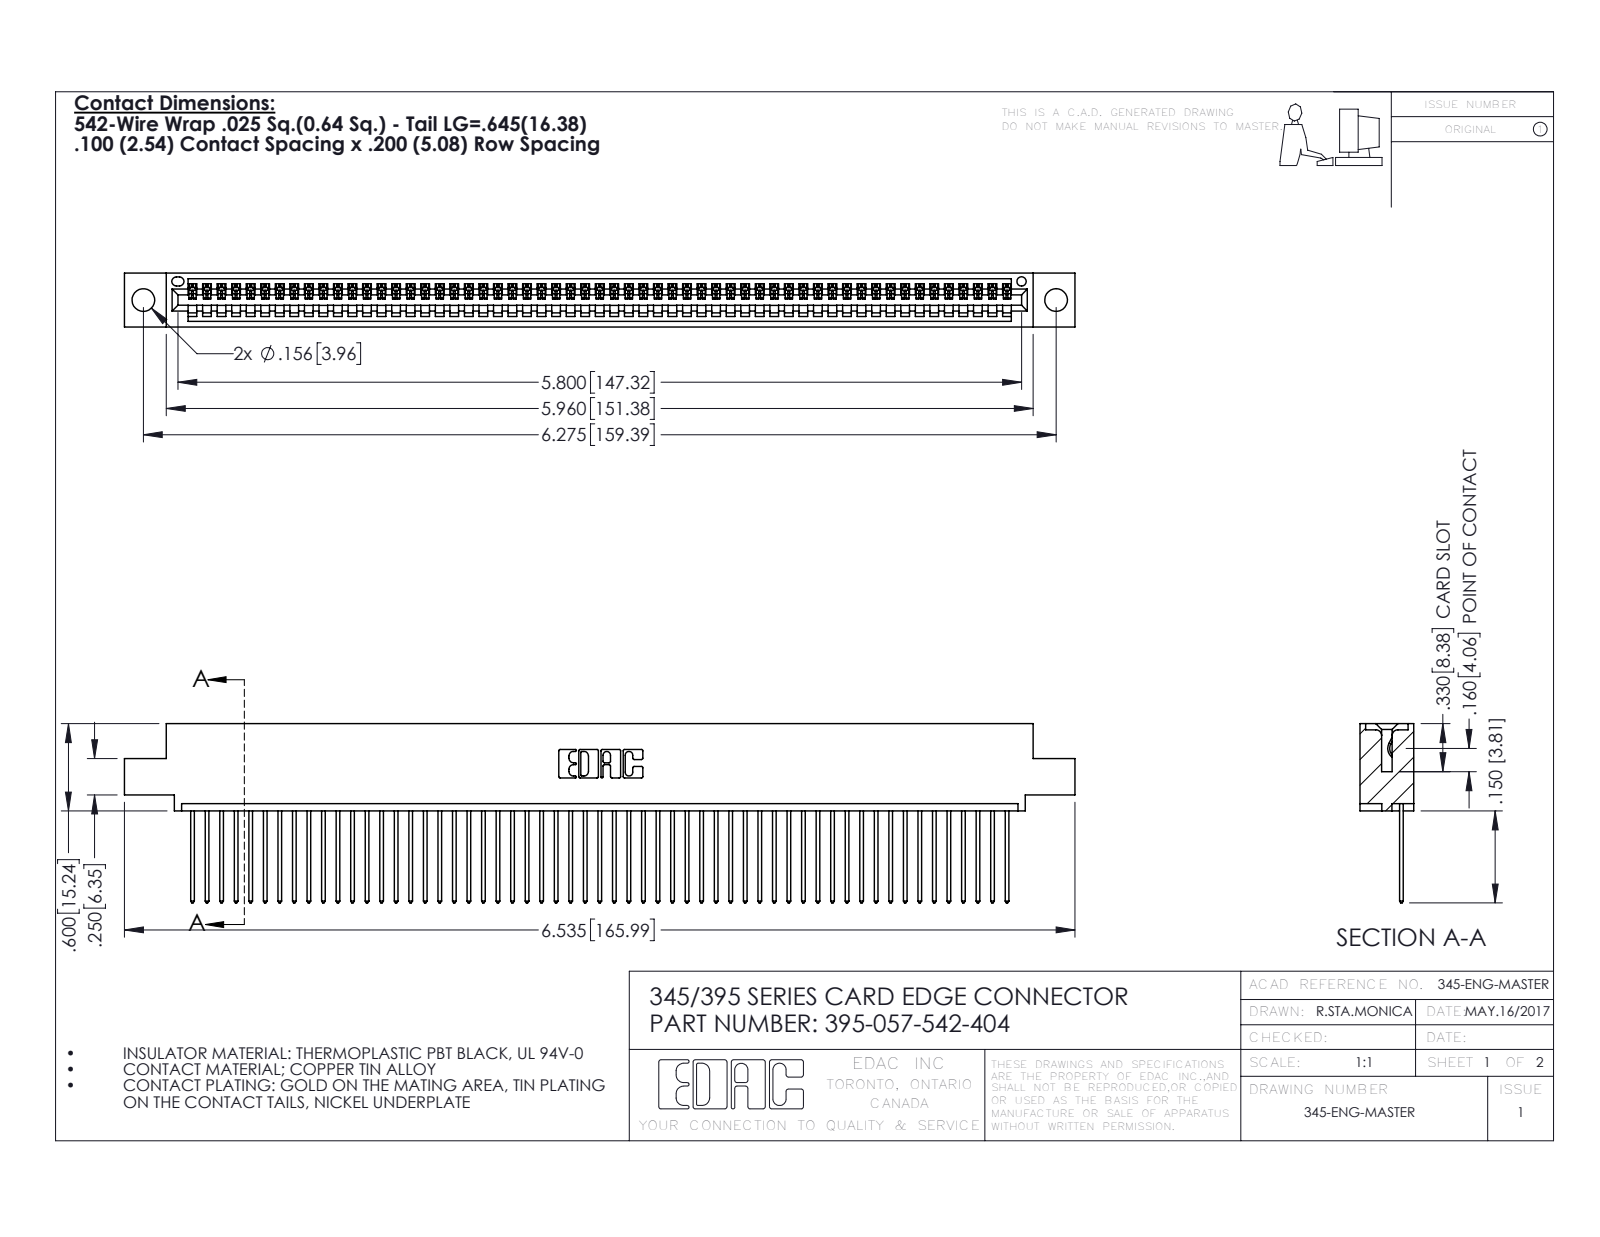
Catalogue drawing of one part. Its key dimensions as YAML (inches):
part_name: "395-057-542-404; 345-292-001_345-293-142; 345 Part_0.110 Offset - 0.156 Dia-TH"
step_written_by: "SolidWorks 2016 (CONFIG_CONTROL_DESIGN)"
units: inches
bodies: {solids: 58, faces: 3436, planar: 2364, cylindrical: 1072, other: 0}
overall_size: [6.535, 1.232, 0.37]
volume: 0.967
surface_area: 34.05
round_holes:
  - {diameter: 0.156, count: 2}
  - {diameter: 0.064, count: 1}
partial_cylinders:
  - {radius: 0.006, count: 114}
  - {radius: 0.01, count: 114}
  - {radius: 0.01, count: 22}
  - {radius: 0.007, count: 6}
  - {radius: 0.031, count: 6}
  - {radius: 0.026, count: 3}
  - {radius: 0.031, count: 2}
  - {radius: 0.04, count: 2}
face_to_face_distances: [0.072, 0.298, 0.098, 0.272, 0.025, 0.37, 0.2, 0.225, 0.149, 0.072]
hole_center_spacings: [0.27, 6.039, 6.275]
